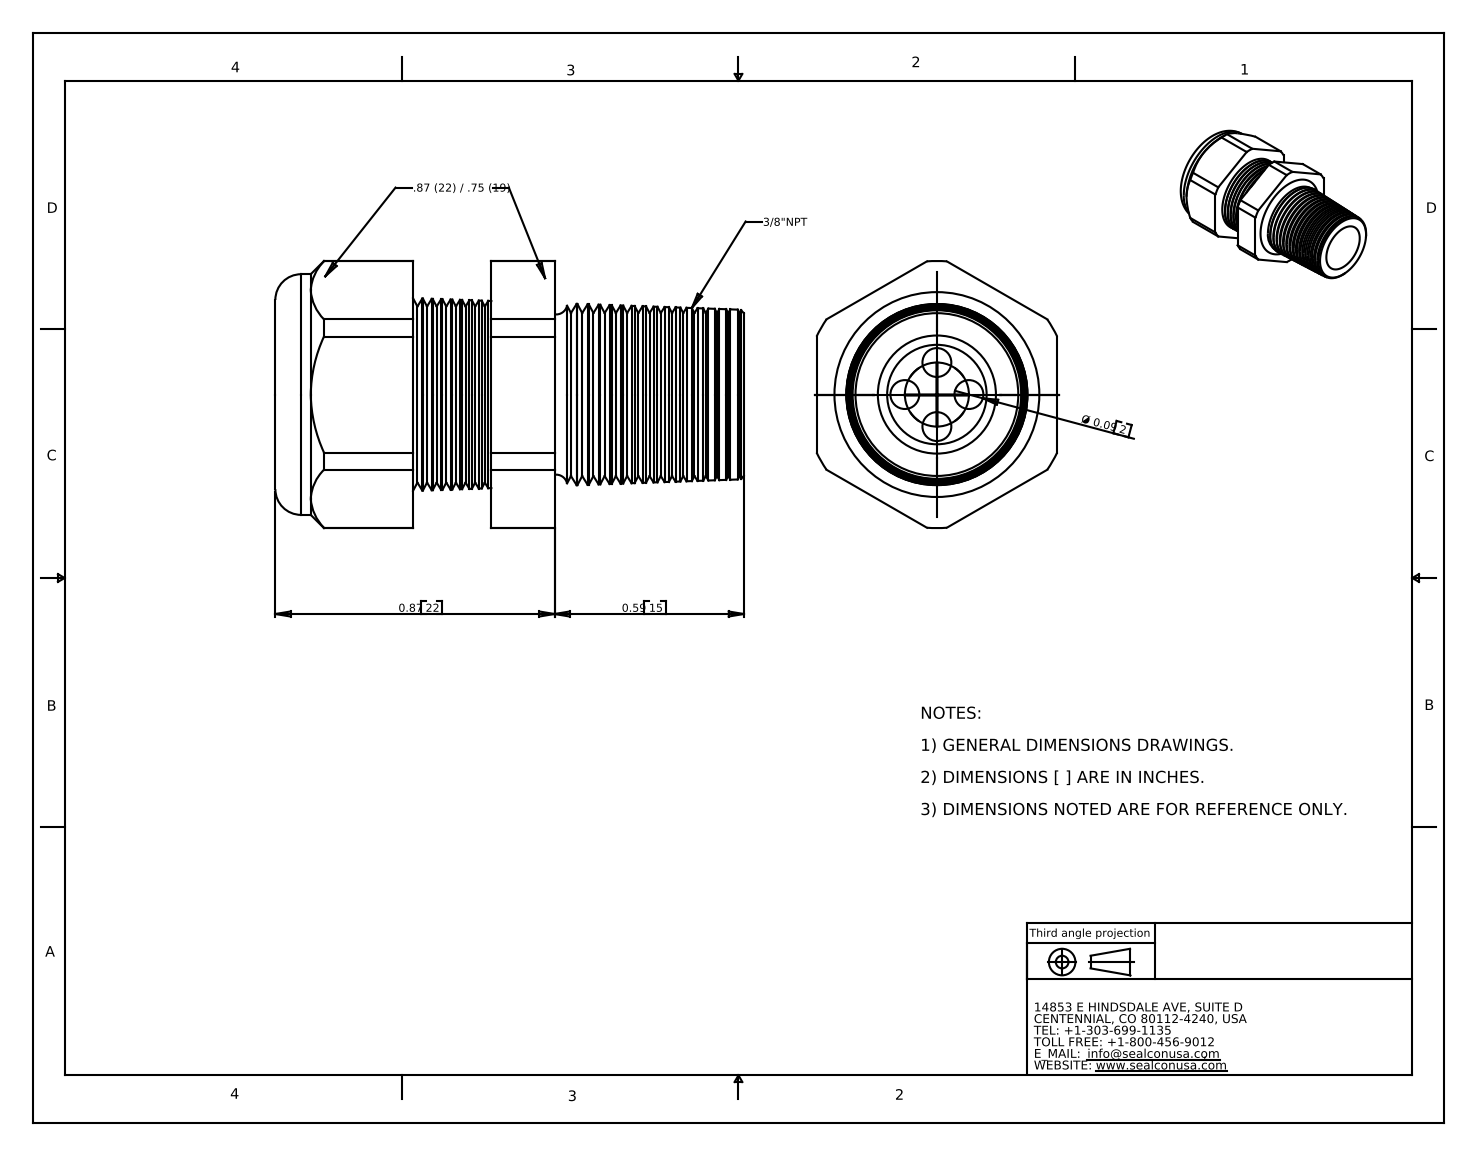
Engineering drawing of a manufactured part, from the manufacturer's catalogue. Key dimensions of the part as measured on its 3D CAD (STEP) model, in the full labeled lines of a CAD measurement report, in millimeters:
Part name (STEP PRODUCT): CD09N9-BK
STEP written by: SolidWorks 2007 (CONFIG_CONTROL_DESIGN)
Units: millimetres
Bodies: 2 solids, 206 faces (20 planar, 28 cylindrical, 158 other)
Overall size (bounding box): 37.1 × 21.2 × 19.1
Volume: 6 010 mm³ · Surface area: 4 550 mm²
Round holes (diameter × count): ⌀2.3 ×4, ⌀7.4 ×1, ⌀7.9 ×1
Round bosses / shafts (diameter × count): ⌀19.1 ×1
Partial cylindrical surfaces — rounded edges, fillets, slot ends (radius × count): R10.6 ×1
Main face-to-face distances: 19.1, 17.1, 10.9, 6.2, 19.1, 22.1, 11.2, 5, 37.1, 26.2
Hole centre spacings: 2.5, 3.6, 5.1
